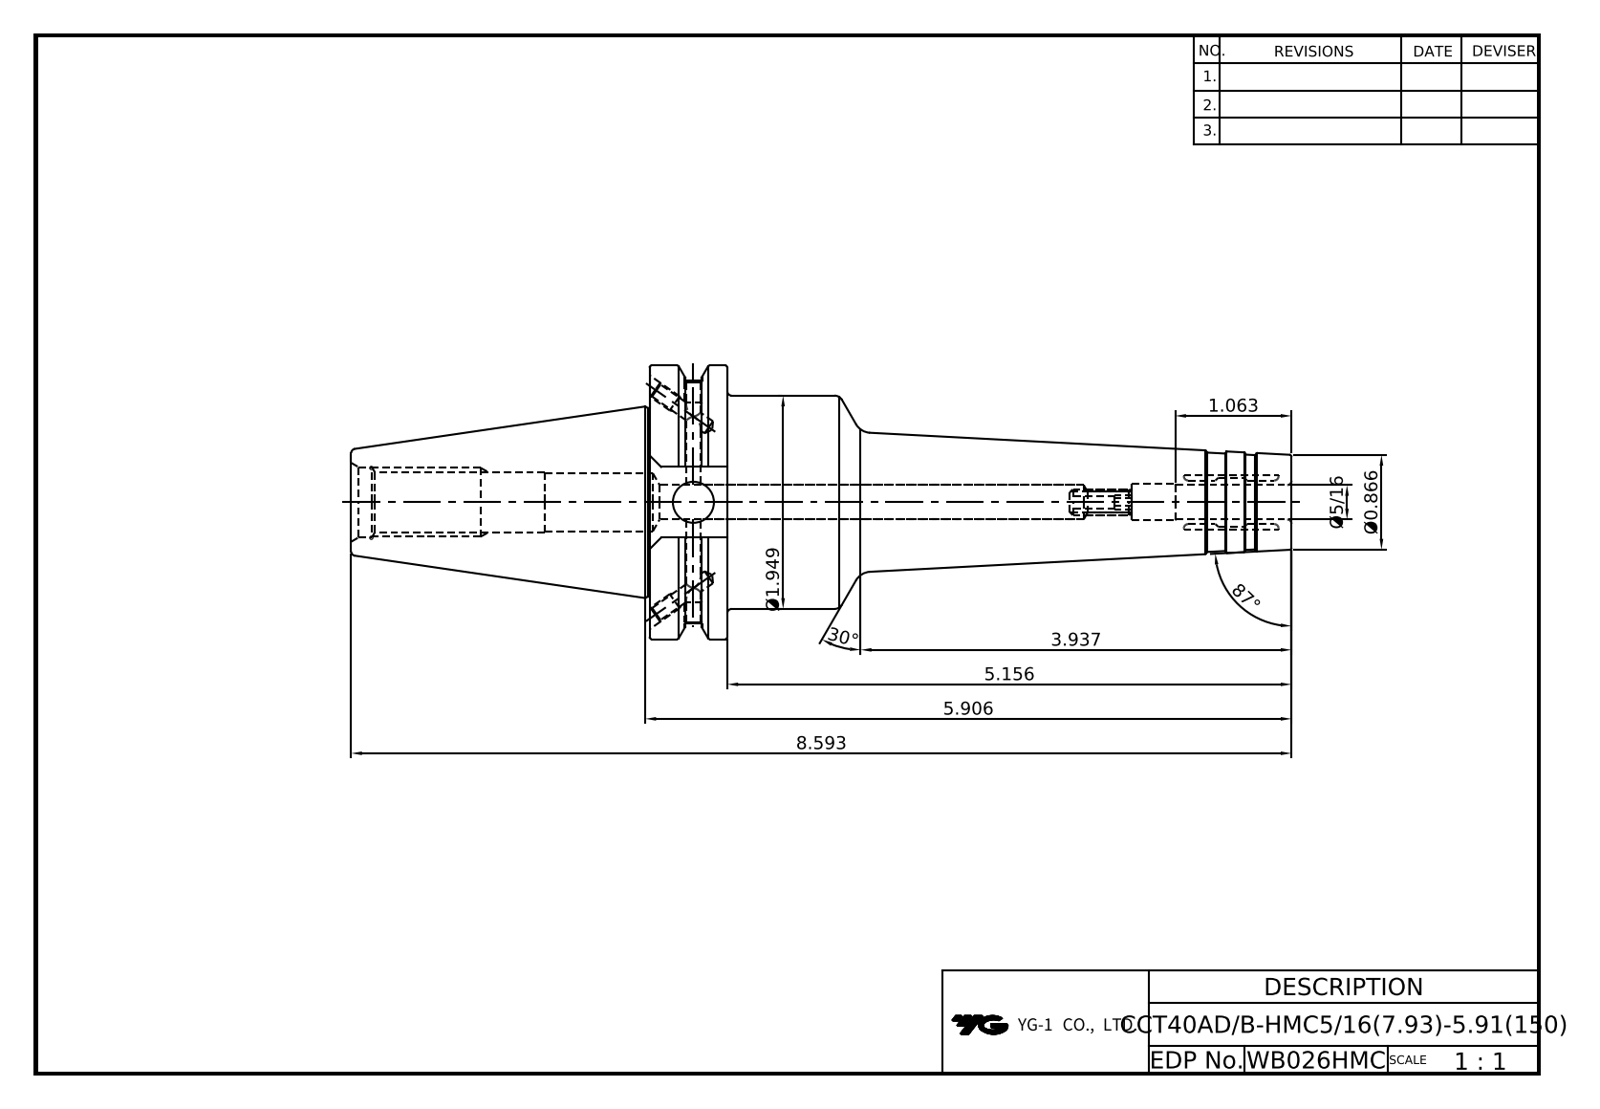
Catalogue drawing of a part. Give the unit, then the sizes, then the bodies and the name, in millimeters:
Units: millimetres
Overall size (bounding box): 218.25 × 63.5 × 61.09
Round holes (diameter × count): ⌀3.24 ×4, ⌀4 ×2, ⌀4.2 ×2, ⌀4.92 ×1, ⌀7.94 ×1, ⌀8 ×1, ⌀9.5 ×1, ⌀9.53 ×1, ⌀13 ×1, ⌀13.39 ×1, ⌀16.3 ×1
Round bosses / shafts (diameter × count): ⌀63.5 ×1, ⌀49.5 ×1
Partial cylindrical surfaces — rounded edges, fillets, slot ends (radius × count): R8.19 ×1, R28.15 ×1
Main face-to-face distances: 18.05, 149, 130.95, 47.6, 16.38, 69.25, 87.3, 218.25, 81.3, 12.05
Volume: 214 165 mm³ · Surface area: 36 357 mm²
Bodies: 1 solid, 107 faces (36 planar, 30 cylindrical, 41 other)
Part name (STEP PRODUCT): LO-CCT40ADB-HMC7.9375-150
STEP written by: Autodesk Inventor 2025 (AUTOMOTIVE_DESIGN)
